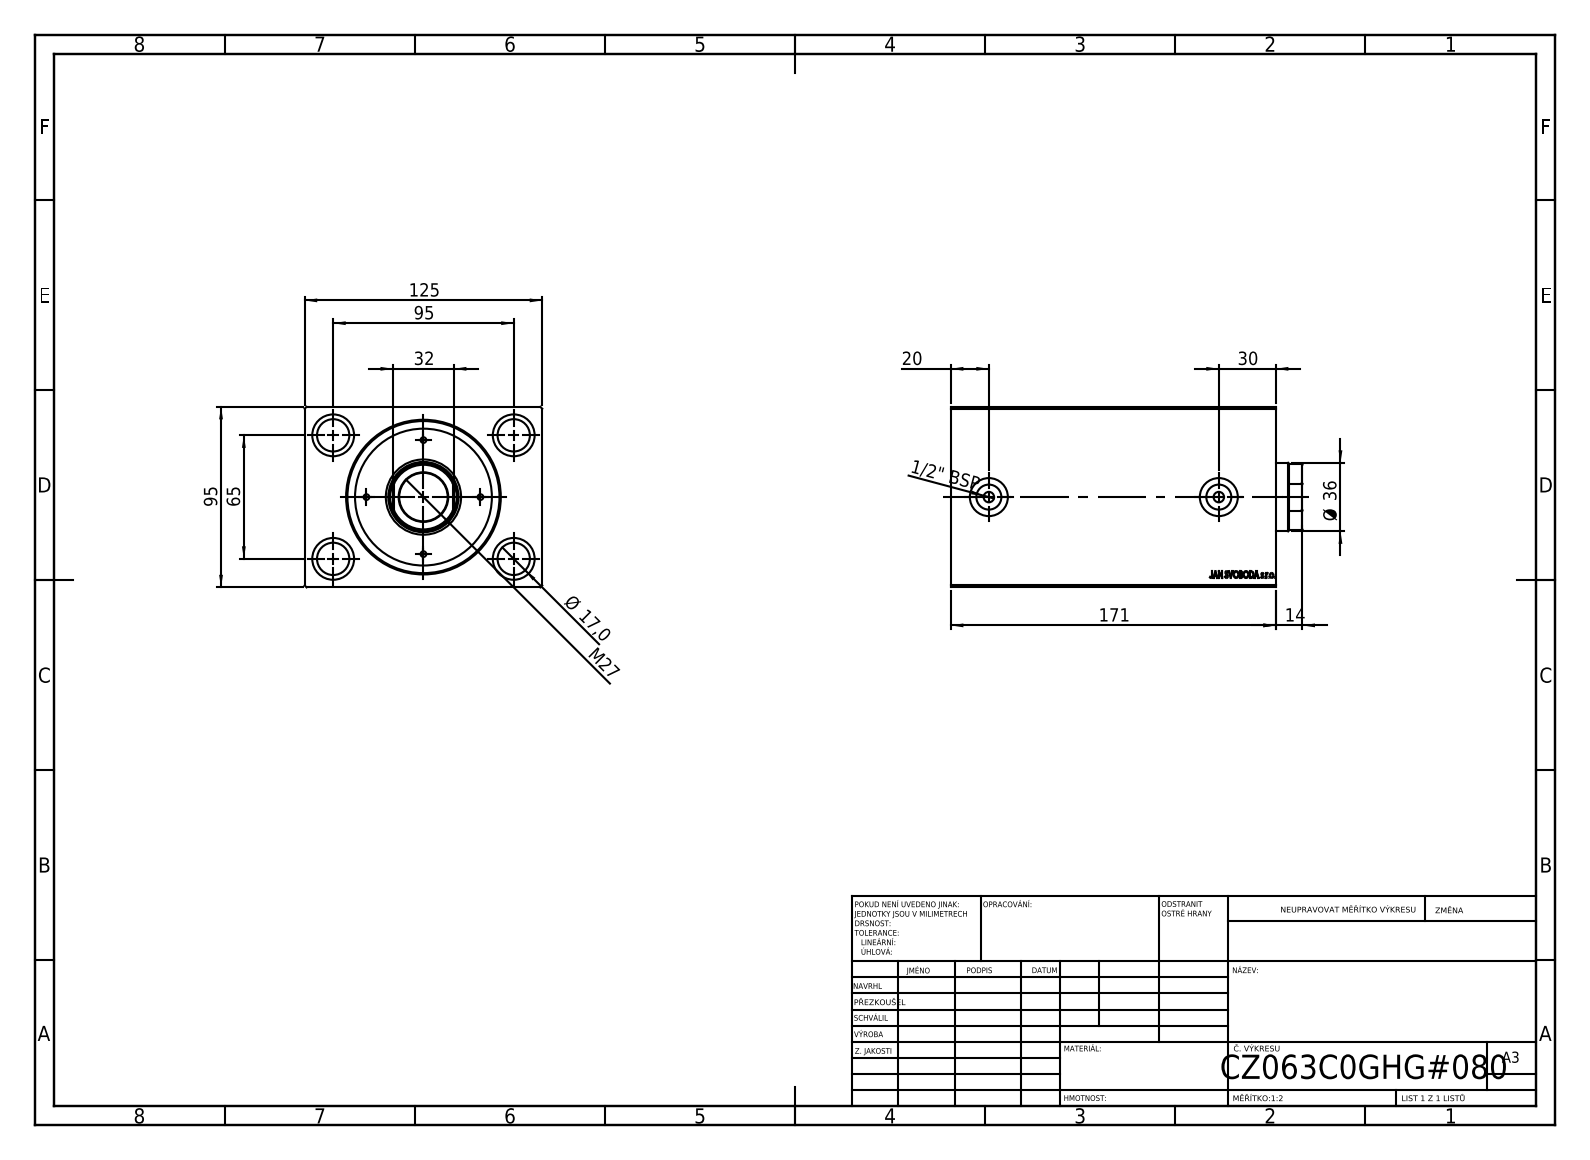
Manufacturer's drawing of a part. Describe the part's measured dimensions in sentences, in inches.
Its 3-D file was written by "SolidWorks 2019 (CONFIG_CONTROL_DESIGN)". It is 1 solid with 825 faces: 397 planar, 46 cylindrical and 382 other. Overall it measures 6.732 by 4.921 by 3.74 inches. Its volume is 83.18 cubic inches and its surface area 258.2 square inches. Round holes: 4 of diameter 0.669, 4 of diameter 0.866, 2 of diameter 0.217, 2 of diameter 0.315, 2 of diameter 0.518, 2 of diameter 0.787, 1 of diameter 1.417, 1 of diameter 2.48, 1 of diameter 3.15. The main face-to-face distances are 3.74, 4.921, 6.732, 5.913, 0.819, 0.551, 5.362, 6.181, 0.407, 6.326. The hole center spacings are 2.266, 2.559, 3.74, 4.532, 3.976, 4.764.
